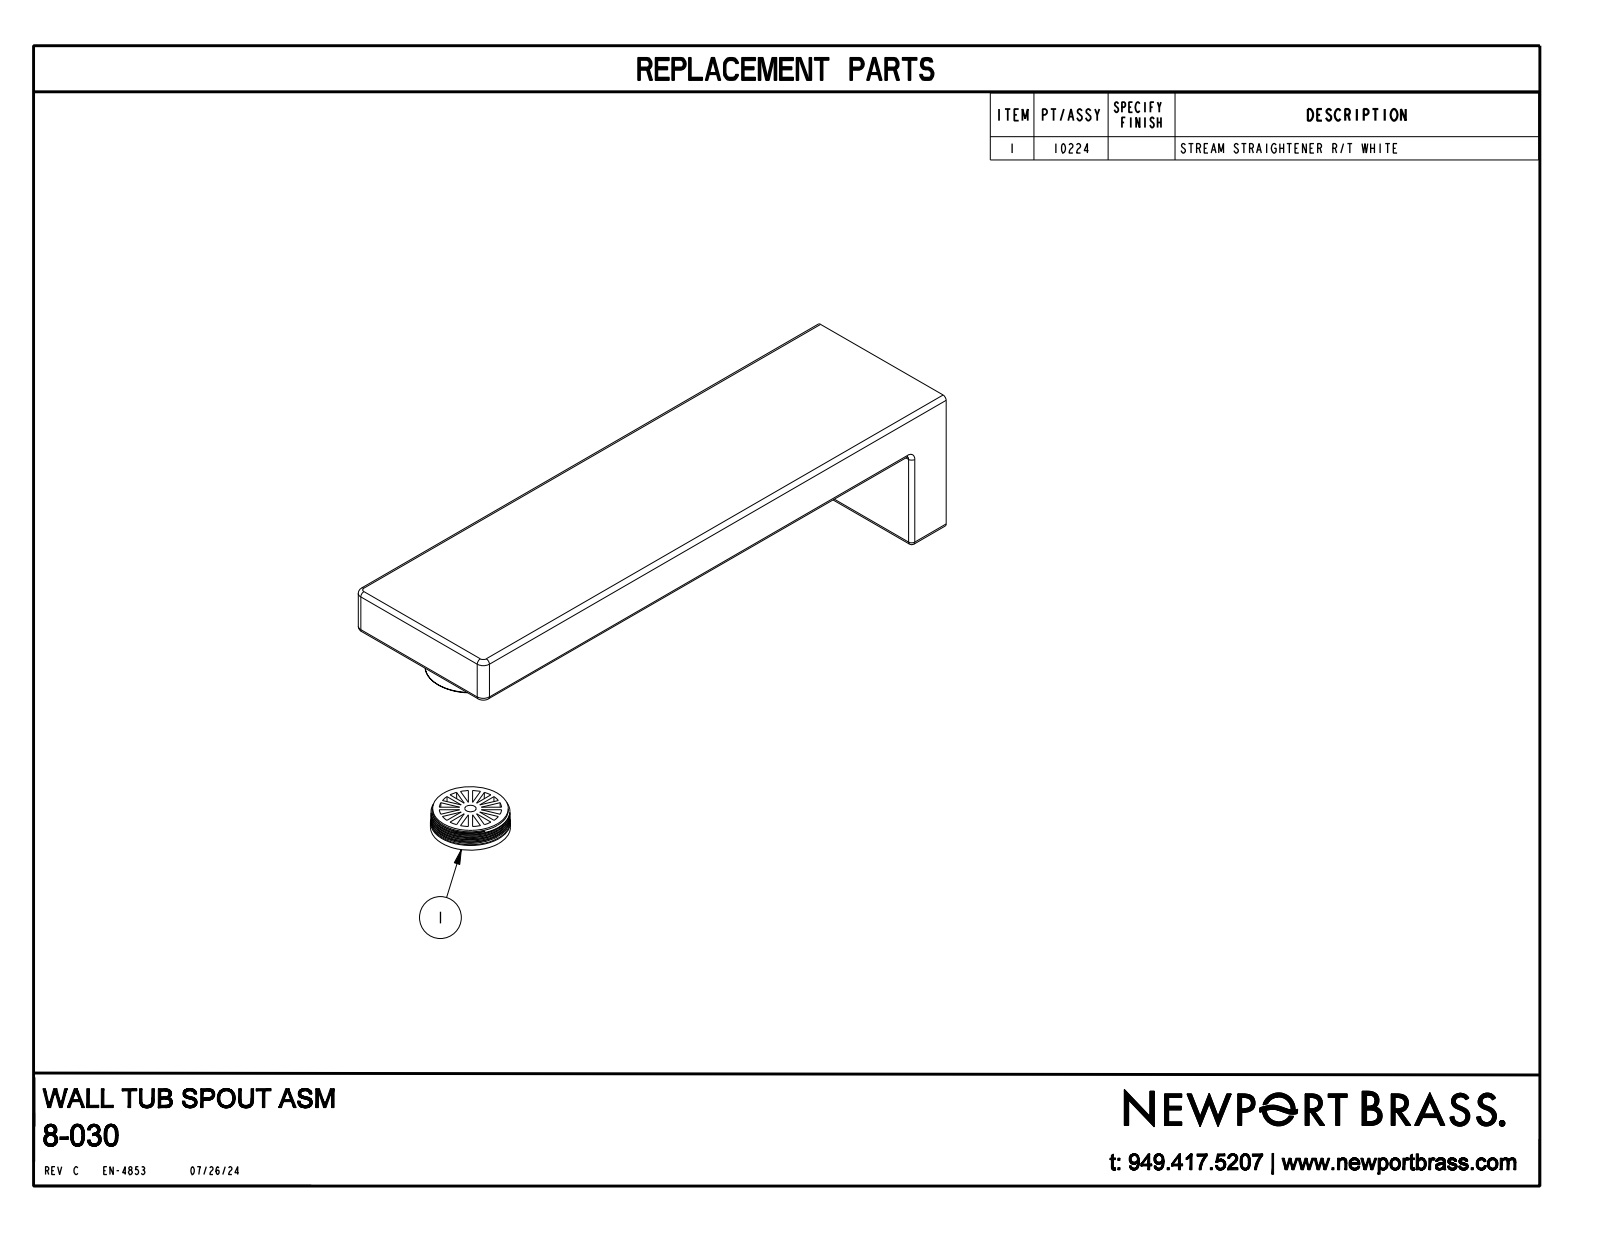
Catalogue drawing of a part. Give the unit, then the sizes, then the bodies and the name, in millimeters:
Units: millimetres
Overall size (bounding box): 239.7 × 63.5 × 55.9
Round bosses / shafts (diameter × count): ⌀45.7 ×1, ⌀32.9 ×1, ⌀31.8 ×1
Partial cylindrical surfaces — rounded edges, fillets, slot ends (radius × count): R1.5 ×11, R3 ×2, R2 ×1
Main face-to-face distances: 17, 63.5, 38.9, 55.9, 11.1, 28.1, 239.7, 228.6, 211.6, 10.9
Volume: 308 200 mm³ · Surface area: 46 770 mm²
Bodies: 1 solid, 41 faces (11 planar, 20 cylindrical, 10 other)
Part name (STEP PRODUCT): 8-030
STEP written by: CREO PARAMETRIC BY PTC INC, 2018400 (AUTOMOTIVE_DESIGN)
